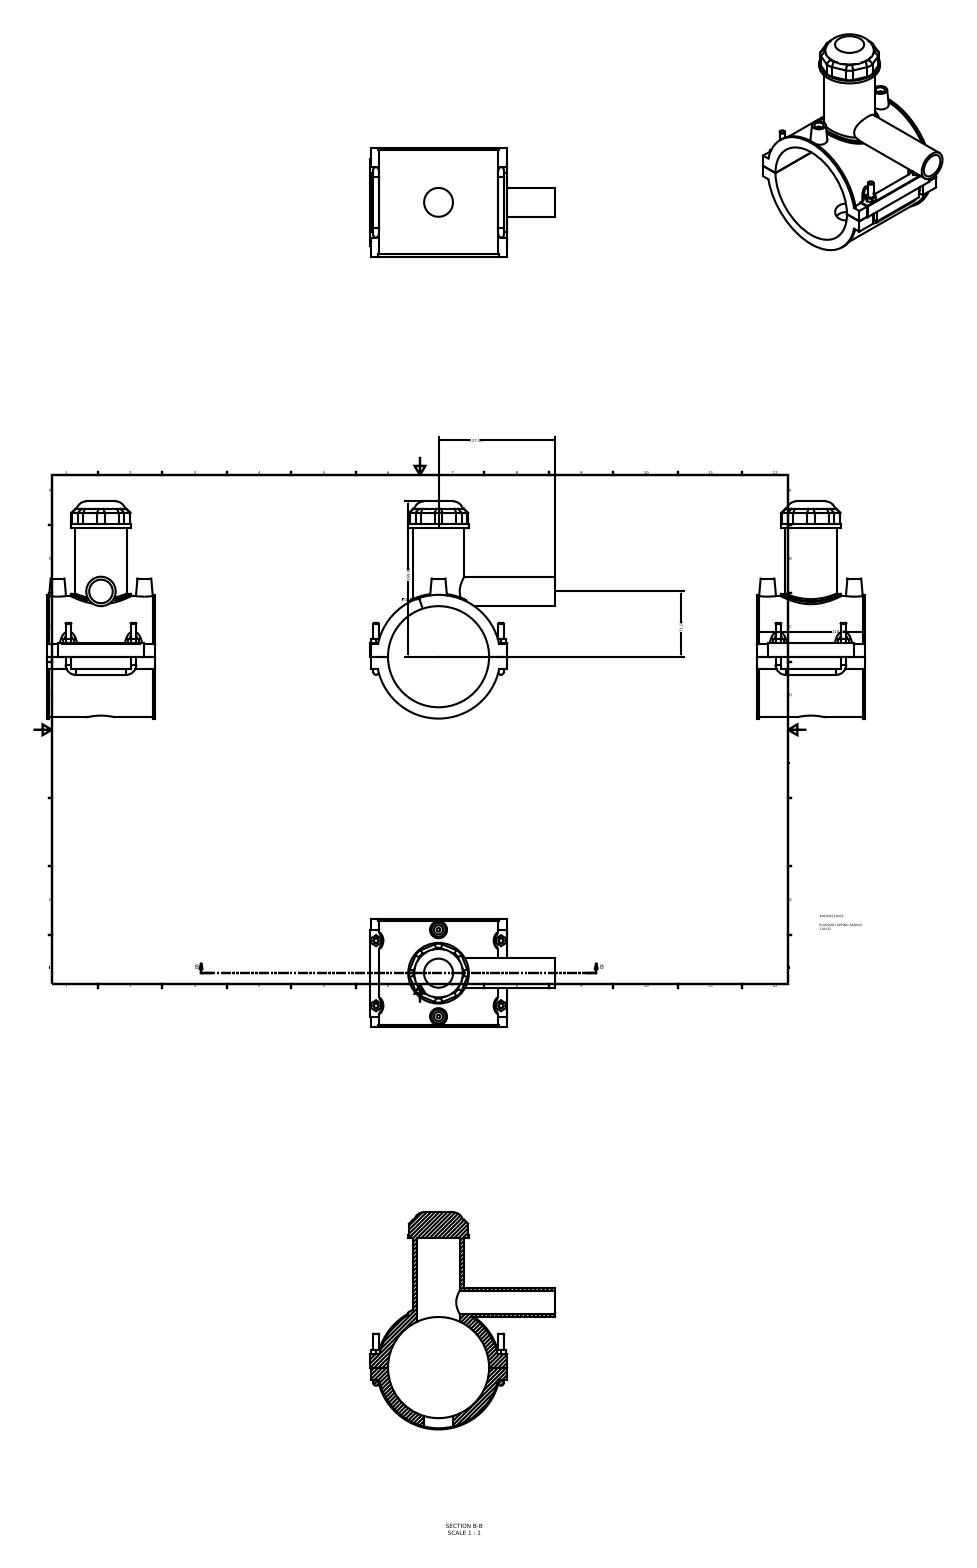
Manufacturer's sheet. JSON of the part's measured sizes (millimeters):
{"part_name": "496304110032", "step_written_by": "Autodesk Inventor 2015 (AUTOMOTIVE_DESIGN)", "units": "millimeters", "bodies": {"solids": 1, "faces": 188, "planar": 117, "cylindrical": 47, "other": 24}, "overall_size": [236.32, 202, 118], "volume_mm3": 705358, "surface_area_mm2": 172705, "round_holes": [[10, 2], [25.6, 1], [31.36, 1], [46.2, 1], [110, 1]], "round_bosses_or_shafts": [[6, 6], [4, 2], [134.64, 1], [132, 1], [66, 1], [56.1, 1], [32, 1]], "partial_cylinders_radius": [[11, 8], [3, 4], [7.5, 4], [0.5, 1], [68.64, 1]], "face_to_face_distances": [118, 1, 154.25, 149, 140.55, 140.45, 28.5, 13.7, 13.8, 14.8], "hole_center_spacings": [47.2, 94.4]}
